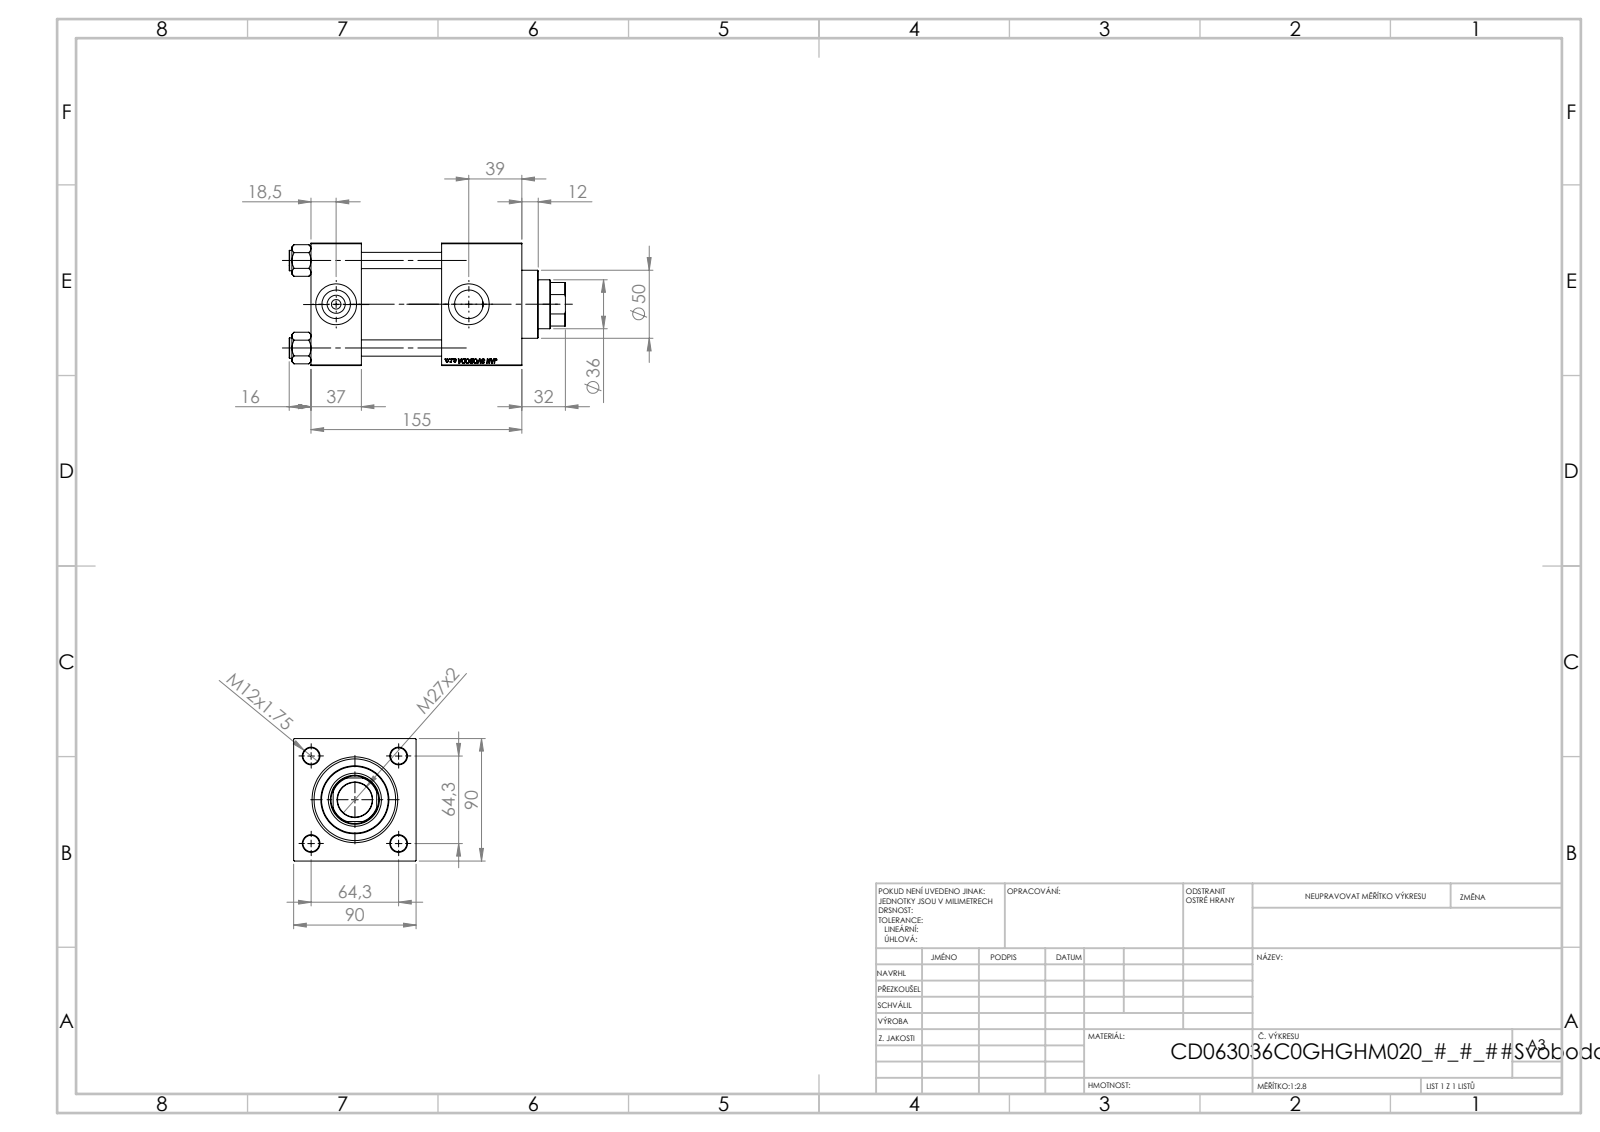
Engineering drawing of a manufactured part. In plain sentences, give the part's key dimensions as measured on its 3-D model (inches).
The part is named "NUT_M5_V215CD_C; V215CD_VC_C; V215CD_VCP_C; V215CD_Body_C (+1 more)". Its 3-D file was written by "SolidWorks 2019 (CONFIG_CONTROL_DESIGN)". It is 11 solids with 1148 faces: 526 planar, 86 cylindrical and 536 other. Overall it measures 7.992 by 3.543 by 3.543 inches. Its volume is 59.07 cubic inches and its surface area 285.6 square inches. Round holes: 4 of diameter 0.472, 2 of diameter 0.276, 2 of diameter 0.825, 2 of diameter 1.181, 1 of diameter 1.004, 1 of diameter 1.417, 1 of diameter 1.535, 1 of diameter 1.969, 1 of diameter 2.362, 1 of diameter 2.48. Round bosses or shafts: 4 of diameter 0.591, 1 of diameter 2.717. Partial cylindrical surfaces (rounded edges, fillets, slot ends): 1 of radius 0.689. The main face-to-face distances are 3.543, 2.323, 1.457, 6.102, 4.646, 3.78, 4.972, 3.516, 1.193, 1.13. The hole center spacings are 1.79, 2.531, 3.58, 3.839.
